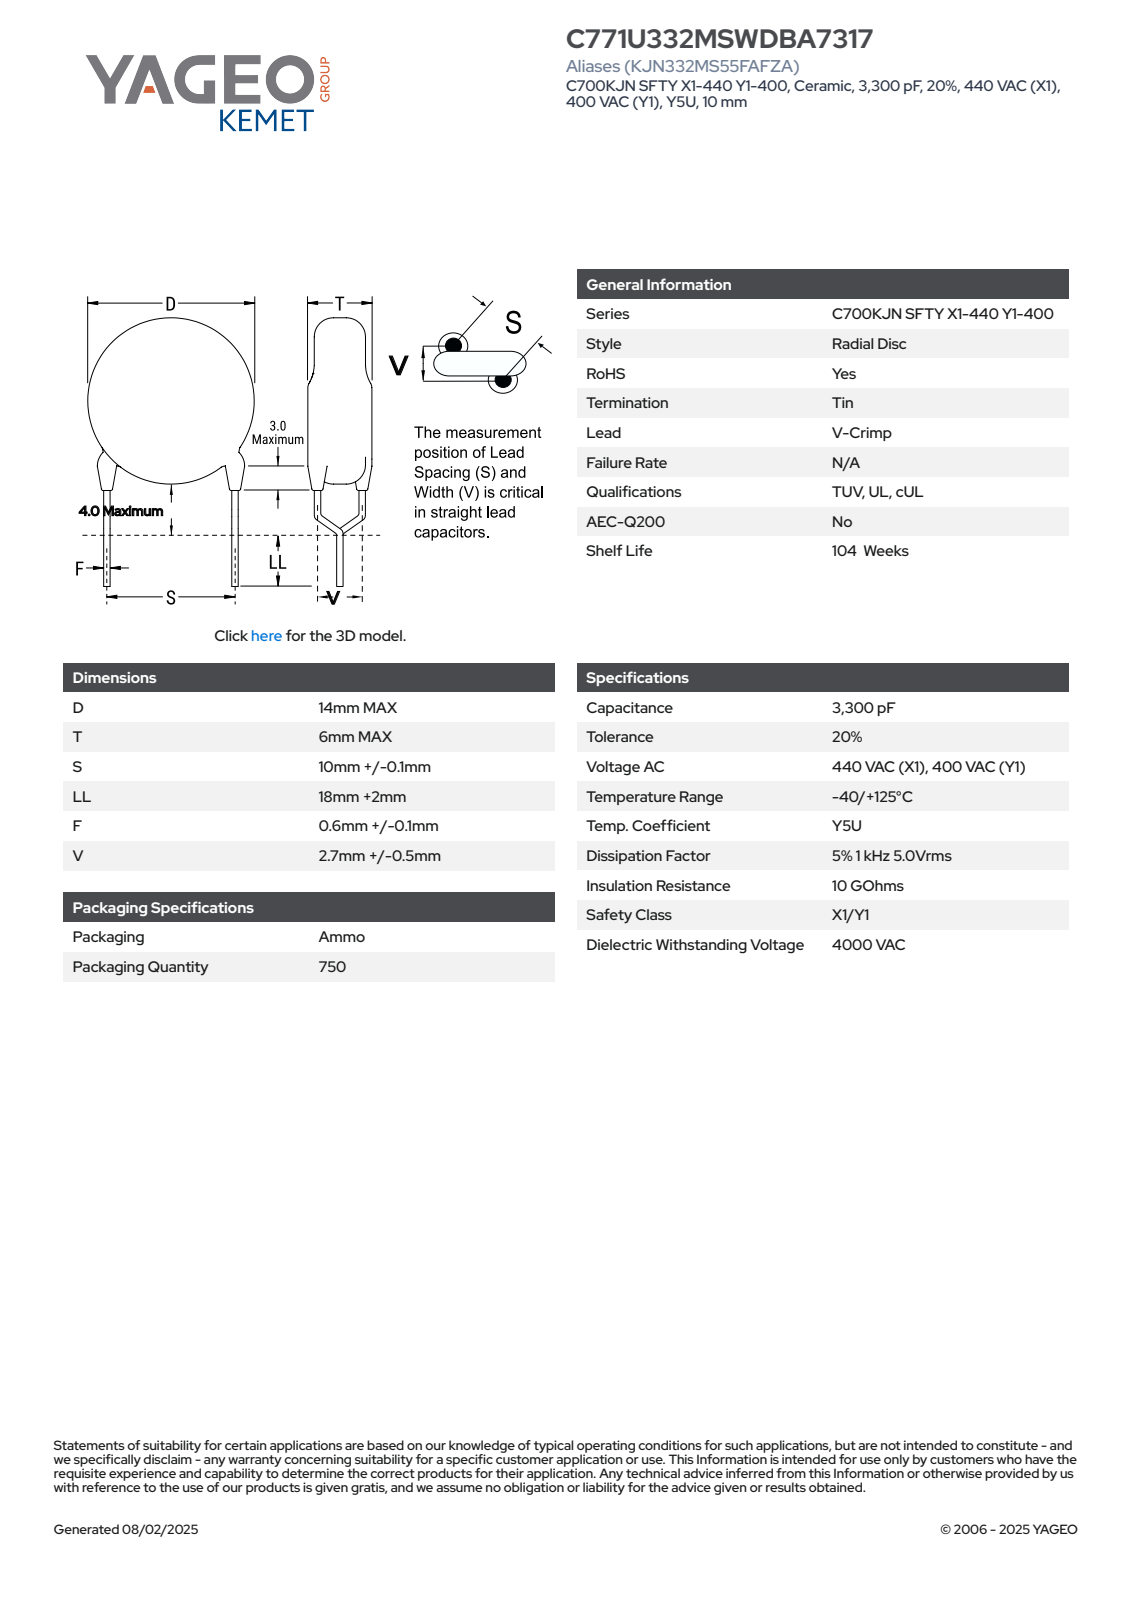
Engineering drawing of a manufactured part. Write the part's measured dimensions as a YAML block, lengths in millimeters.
part_name: "CCD_VC14X6_D14T6S10LL20F0.7V2.7"
step_written_by: "SolidWorks 2021 (AUTOMOTIVE_DESIGN)"
units: millimeters
bodies: {solids: 4, faces: 85, planar: 63, cylindrical: 18, other: 4}
overall_size: [34, 14, 6]
volume: 926
surface_area: 662
round_bosses_or_shafts:
  - {diameter: 0.7, count: 6}
  - {diameter: 1.2, count: 2}
  - {diameter: 14, count: 1}
face_to_face_distances: [6, 20, 28.35, 8.35, 26.41, 6.41, 1.94, 0.53, 7.93, 0.37]
